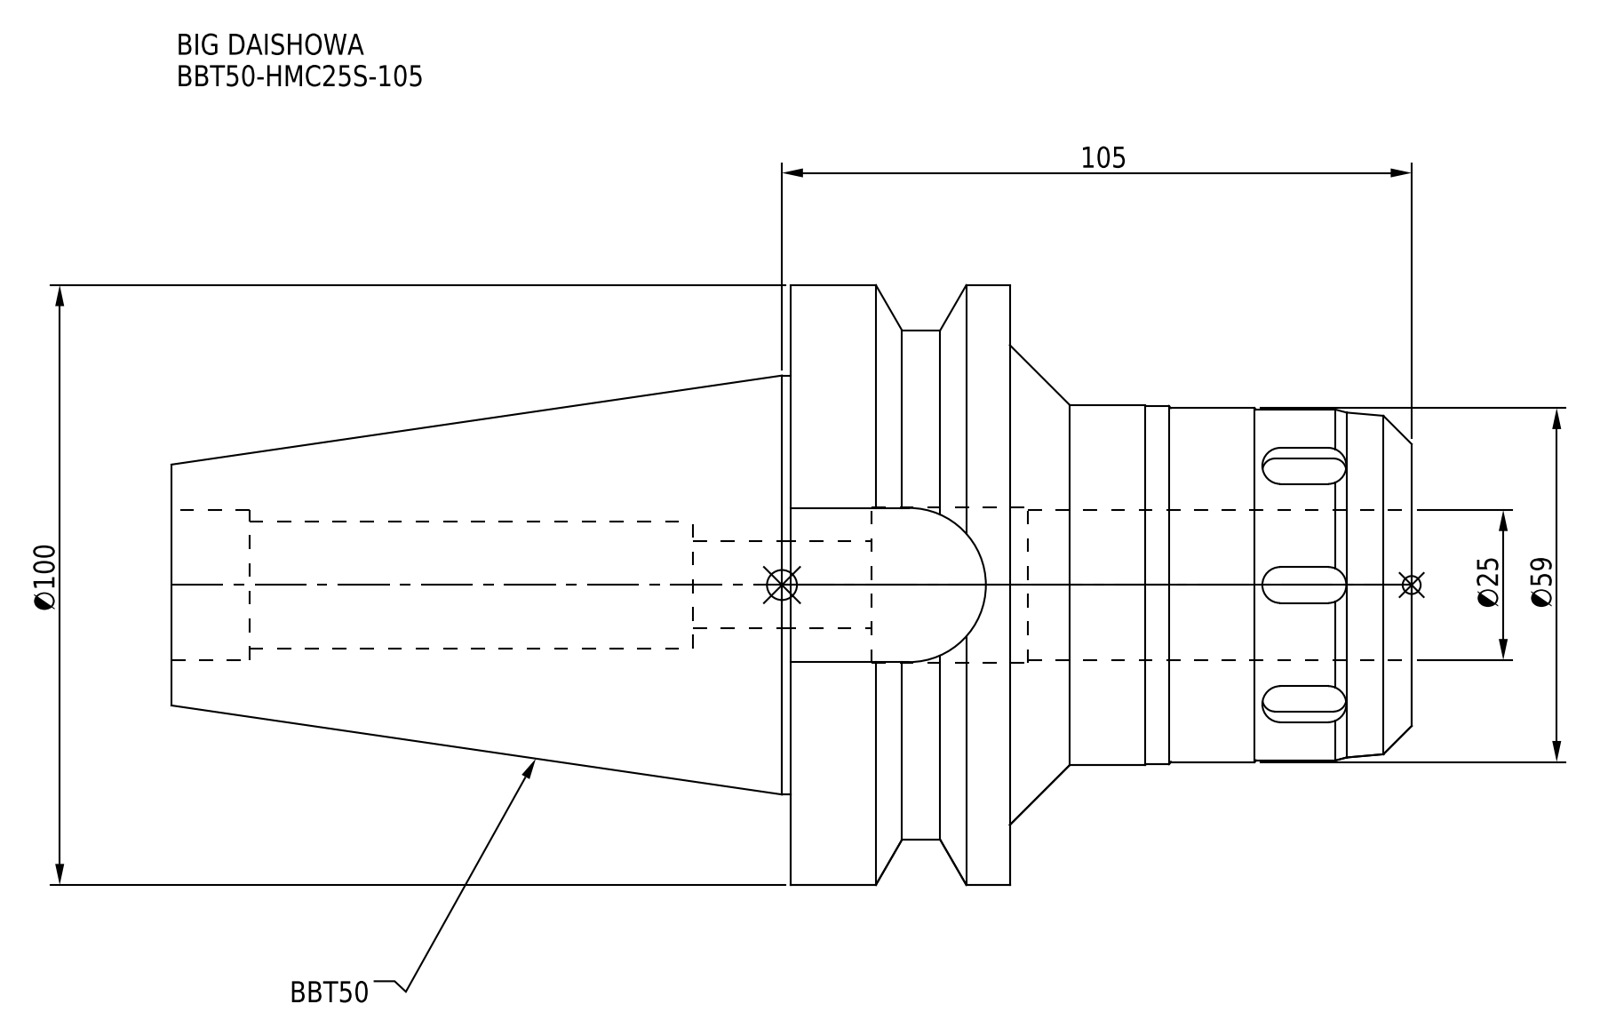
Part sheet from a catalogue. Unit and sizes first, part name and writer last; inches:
Units: inches
Overall size (bounding box): 8.142 × 3.937 × 3.937
Round holes (diameter × count): ⌀0.571 ×1, ⌀0.835 ×1, ⌀0.984 ×1, ⌀1.024 ×1
Round bosses / shafts (diameter × count): ⌀3.937 ×1, ⌀3.346 ×1, ⌀2.75 ×1, ⌀2.362 ×1, ⌀2.35 ×1, ⌀2.323 ×1, ⌀2.303 ×1
Partial cylindrical surfaces — rounded edges, fillets, slot ends (radius × count): R0.118 ×12, R0.506 ×1
Main face-to-face distances: 1.437, 2.638, 4.075, 8.142, 5.504, 4.067, 2.787, 1.012, 3.543, 0.906
Volume: 36.99 in³ · Surface area: 109.7 in²
Bodies: 1 solid, 101 faces (39 planar, 44 cylindrical, 18 other)
Part name (STEP PRODUCT): BBT50-HMC25S-105
STEP written by: CREO PARAMETRIC BY PTC INC, 2016380 (AUTOMOTIVE_DESIGN)
